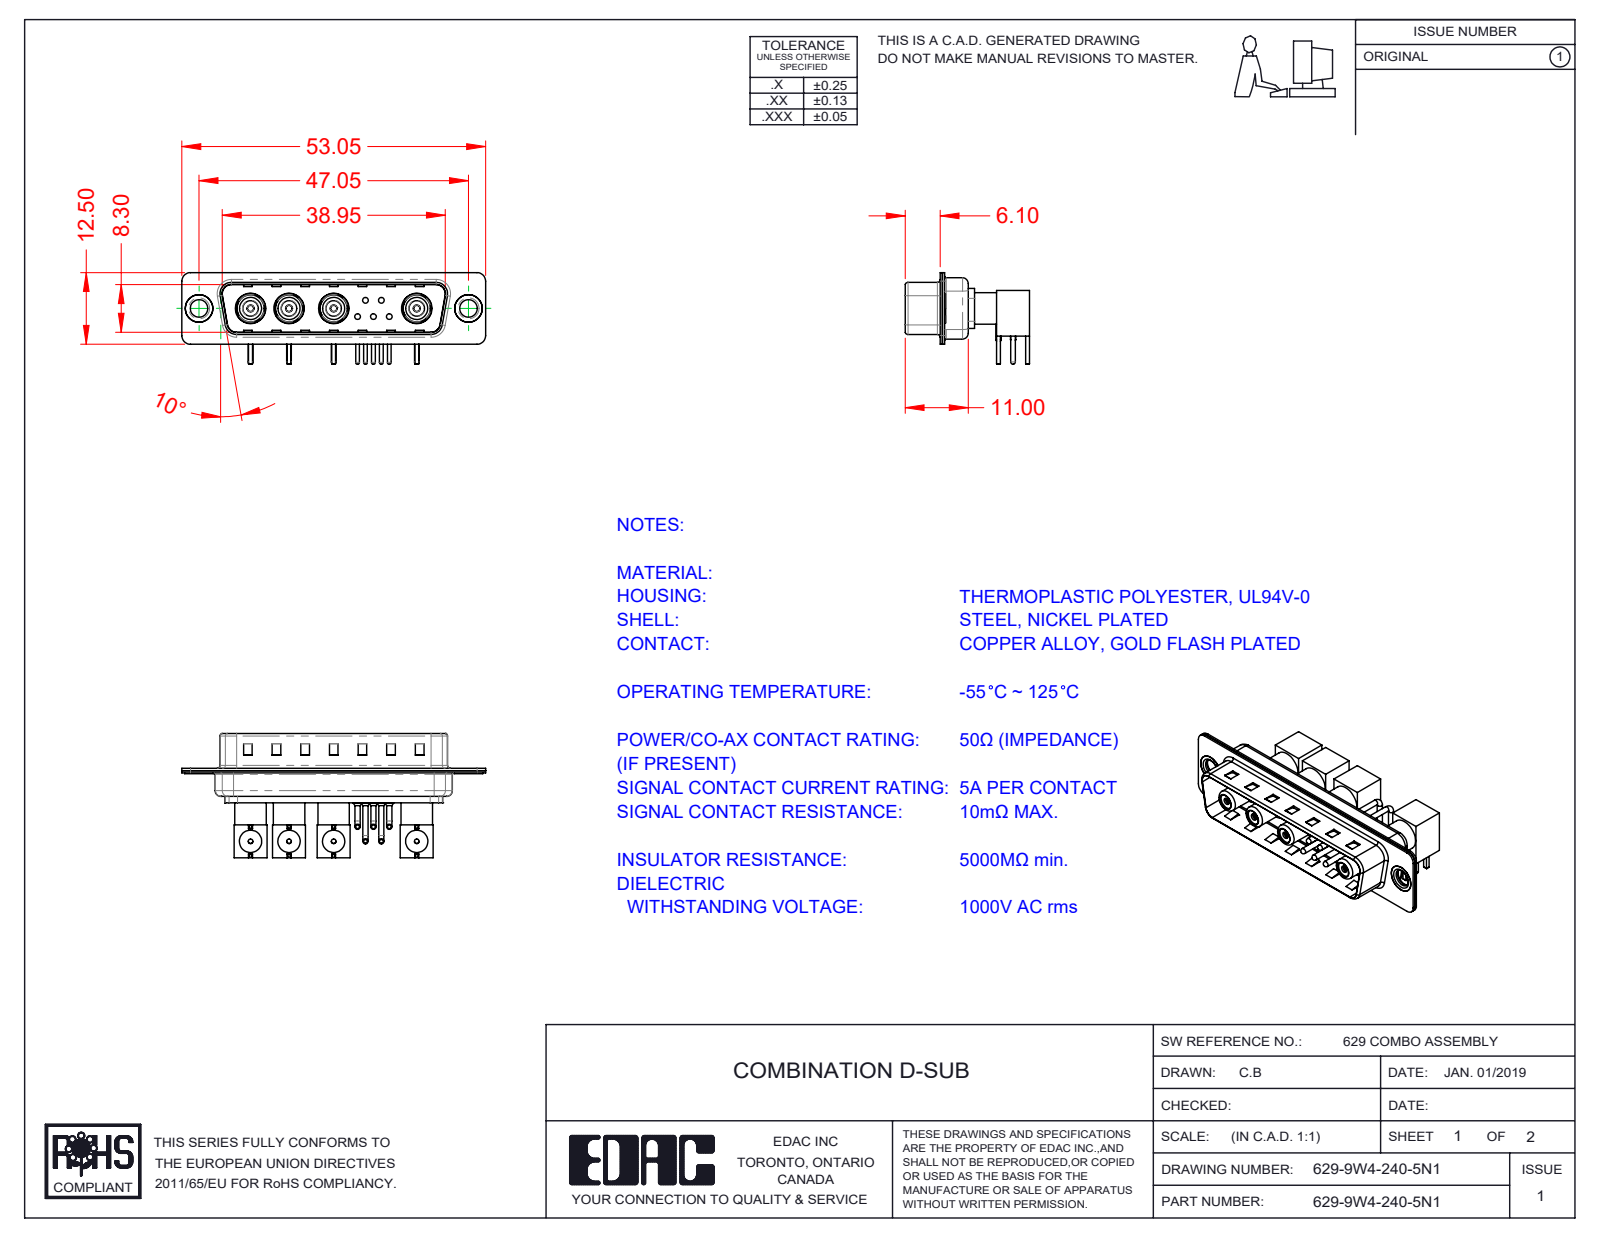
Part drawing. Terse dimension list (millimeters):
name: Co-Ax Jack_RA PC Tail; Co-Ax Jack Assy_RA; 629Combo Shell Rear_25 Contacts; 629Combo Housing_9W4 (+8 more)
written by: SolidWorks 2020 (CONFIG_CONTROL_DESIGN)
unit: mm
bodies: 38 solids, 1508 faces (719 planar, 569 cylindrical, 220 other)
size: 53.05 × 21.71 × 16
volume: 3 820 mm³; area: 10 484 mm²
holes: 9× ⌀1.6, 5× ⌀0.75, 5× ⌀2, 4× ⌀0.8, 4× ⌀1.1, 4× ⌀1.2, 4× ⌀1.5, 4× ⌀2.5, 4× ⌀2.7, 4× ⌀3.1, 4× ⌀3.4, 4× ⌀3.9
bosses: 10× ⌀0.9, 8× ⌀0.8, 5× ⌀1.5, 5× ⌀1, 5× ⌀0.65, 4× ⌀5.5, 4× ⌀5.2, 4× ⌀4.8
rounds: 16× R1.5, 12× R2, 8× R0.5, 8× R1.6, 5× R1.01, 4× R0.25, 4× R0.6, 4× R0.65
face distances: 0.4, 0.8, 9.5, 5.75, 9.1, 8.7, 9.9, 0.35, 1.4, 0.45
hole spacings: 14.51, 14.52, 6.72, 7.79, 7.8, 22.31, 29.03, 3.16
